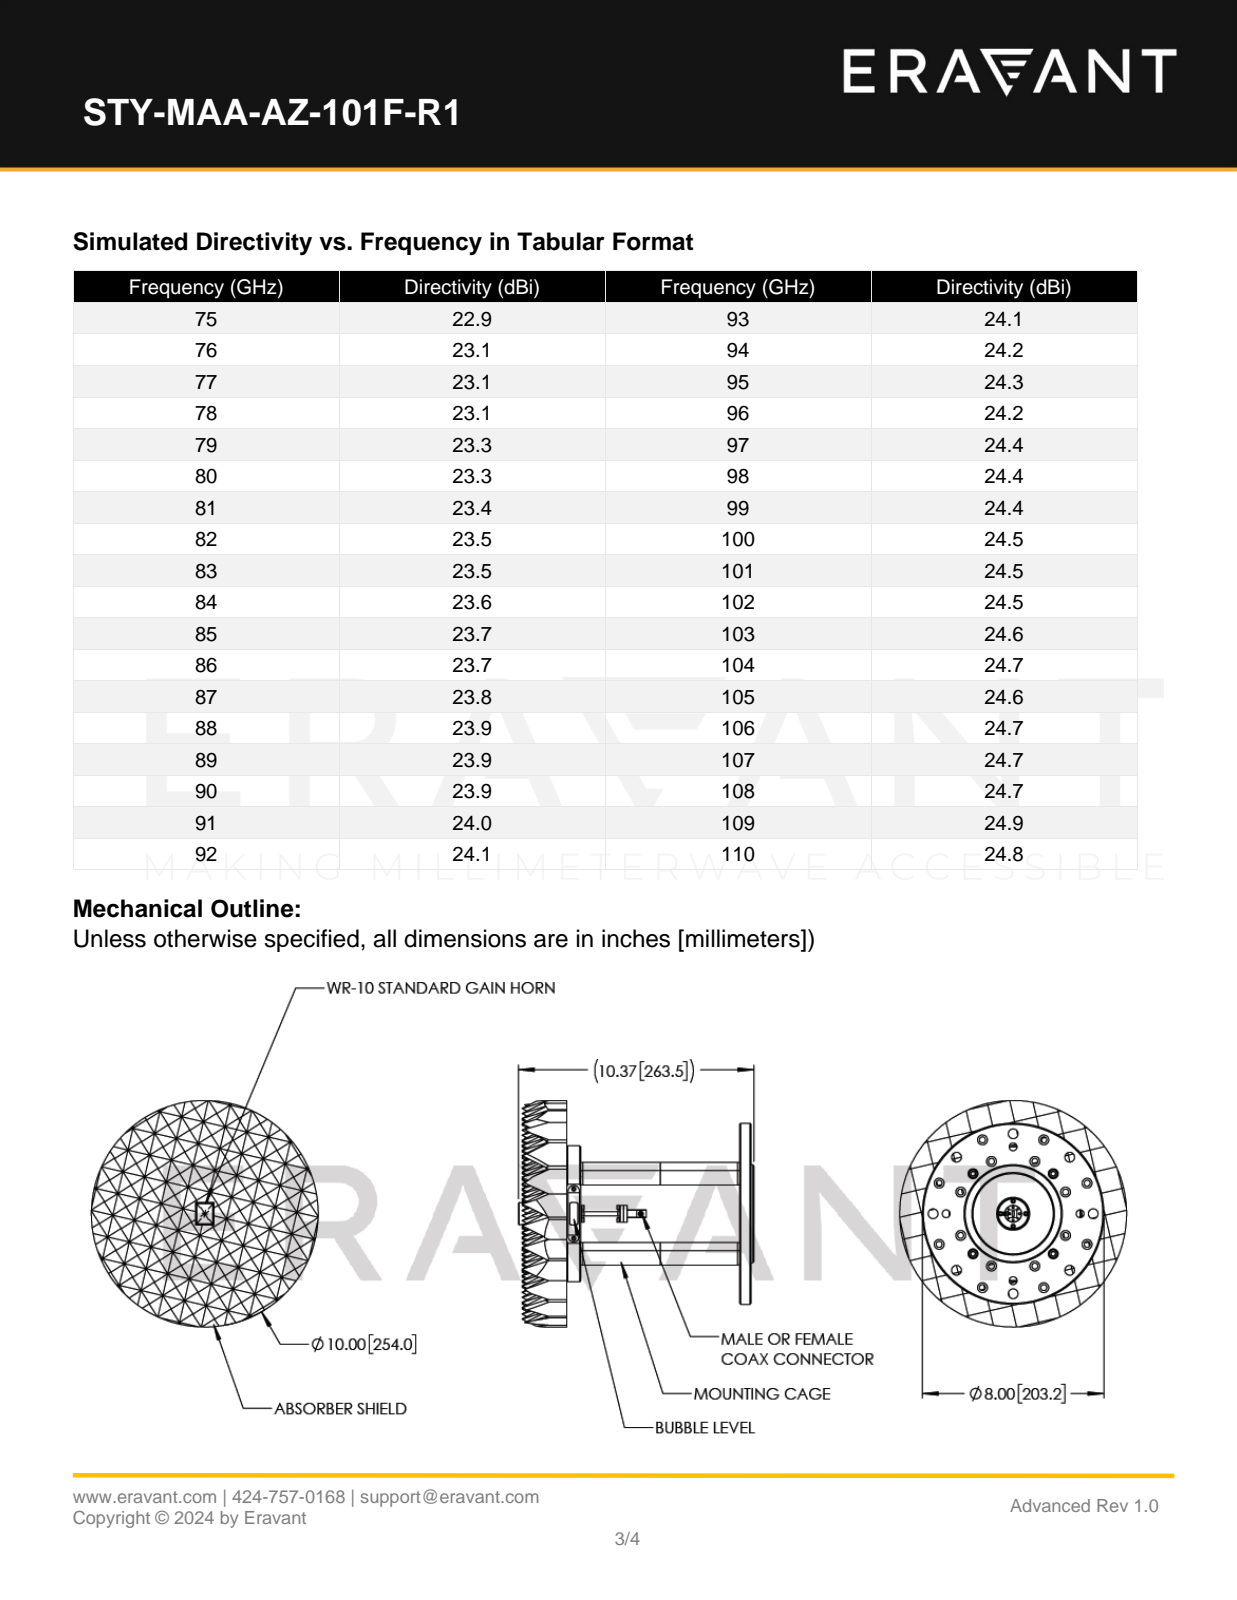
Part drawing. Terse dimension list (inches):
name: STY-MAA-AZ-101F-R1
written by: SolidWorks 2021 (CONFIG_CONTROL_DESIGN)
unit: in
bodies: 88 solids, 1497 faces (664 planar, 352 cylindrical, 481 other)
size: 10.374 × 10 × 10
volume: 151.7 in³; area: 787.5 in²
holes: 20× ⌀0.266, 16× ⌀0.437, 8× ⌀0.433, 4× ⌀0.348, 4× ⌀0.75, 2× ⌀0.089, 2× ⌀0.125, 1× ⌀0.039, 1× ⌀0.094, 1× ⌀1.4, 1× ⌀3.543
bosses: 4× ⌀1, 4× ⌀0.437, 4× ⌀0.18, 3× ⌀0.08, 1× ⌀10, 1× ⌀8, 1× ⌀6, 1× ⌀4.331
rounds: 48× R0.005, 2× R0.08, 2× R0.25, 1× R0.005, 1× R0.107, 1× R0.24
face distances: 0.984, 1.969, 0.985, 1.969, 2.953, 2.953, 3.937, 0.984, 4.922, 3.937
hole spacings: 4.326, 5.585, 3.458, 5.046, 5.918, 1.551, 2.496, 3.53
